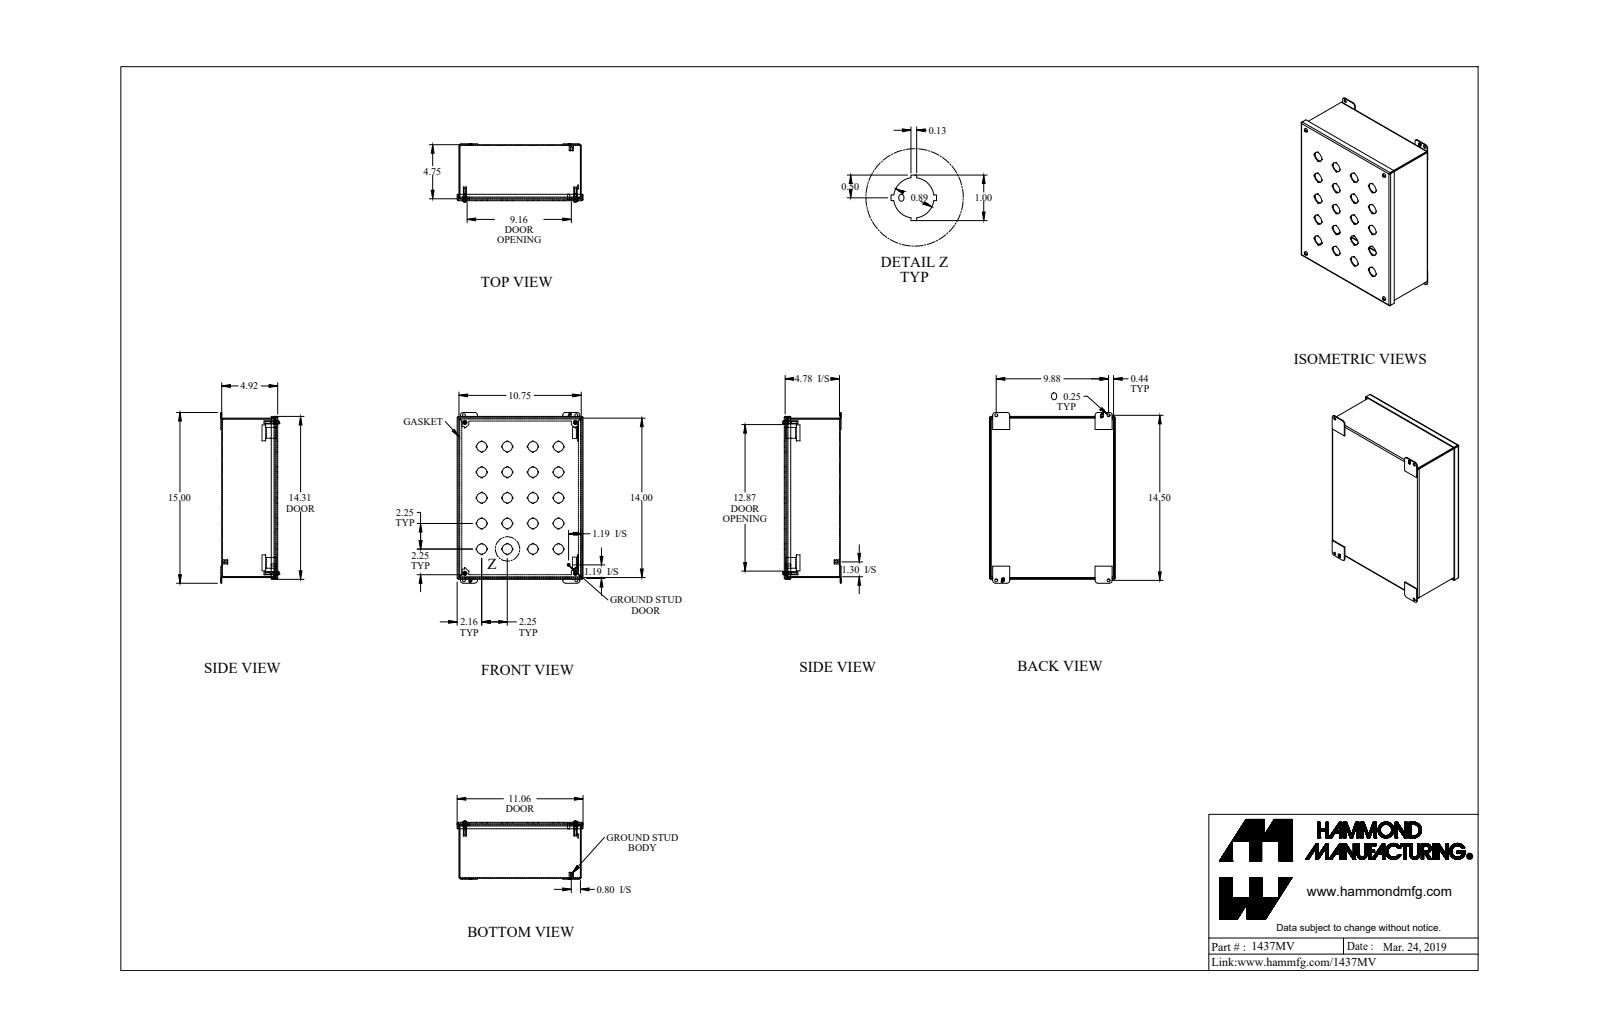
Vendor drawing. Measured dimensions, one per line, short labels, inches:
name: 1437MV_Default
written by: SolidWorks 2019 (CONFIG_CONTROL_DESIGN)
unit: in
bodies: 23 solids, 1035 faces (739 planar, 240 cylindrical, 56 other)
size: 15 × 11.062 × 5.121
volume: 45.74 in³; area: 1 226 in²
holes: 20× ⌀0.886, 8× ⌀0.25, 4× ⌀0.159, 4× ⌀0.406, 1× ⌀0.156
bosses: 4× ⌀0.39, 4× ⌀0.275, 4× ⌀0.19, 4× ⌀0.148, 1× ⌀0.375, 1× ⌀0.25, 1× ⌀0.188
rounds: 12× R0.036, 12× R0.108, 8× R0.25, 4× R0.029, 4× R0.086, 4× R0.16, 4× R0.171, 2× R0.125
face distances: 0.072, 4.85, 4.922, 4.778, 10.678, 13.928, 10.75, 10.606, 14, 13.856
hole spacings: 2.25, 5.031, 3.182, 4.5, 7.115, 0.63, 6.364, 6.75
